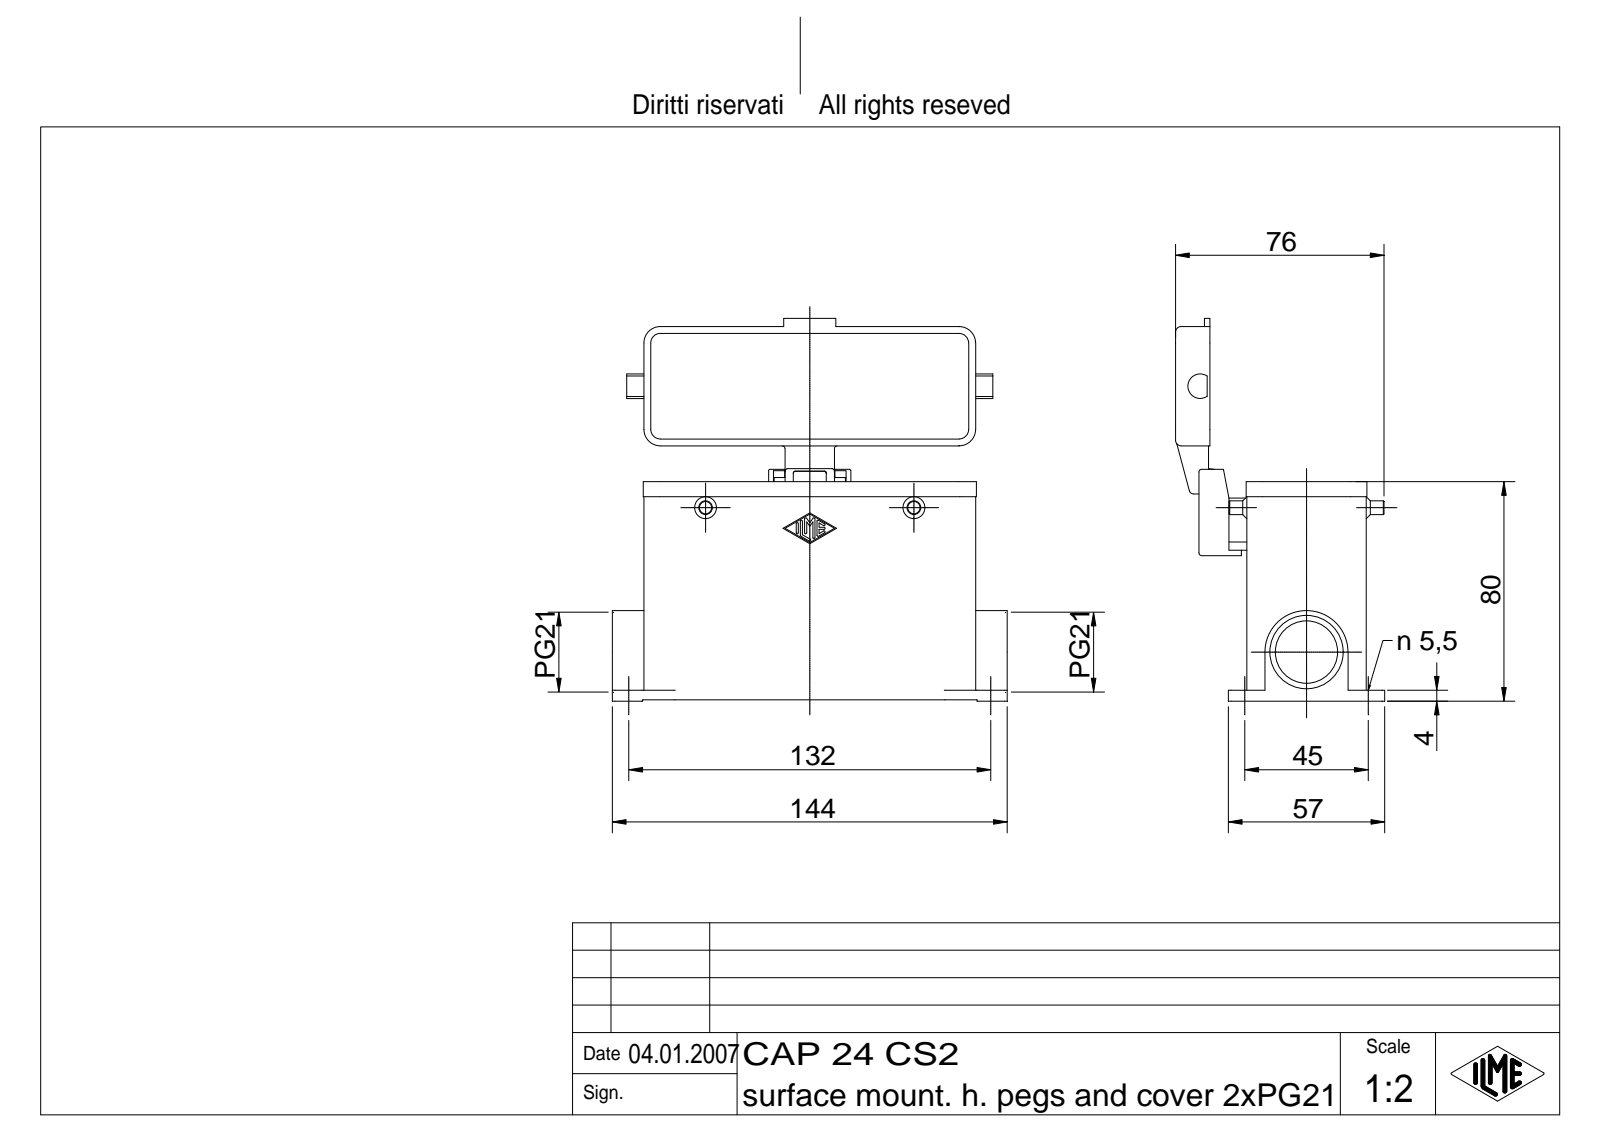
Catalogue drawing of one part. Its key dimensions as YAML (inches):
part_name: "CAP 24 CS2"
step_written_by: "Autodesk Inventor 7 (AUTOMOTIVE_DESIGN)"
units: inches
bodies: {solids: 2, faces: 474, planar: 177, cylindrical: 177, other: 120}
overall_size: [5.669, 5.492, 3.002]
volume: 9.798
surface_area: 136.9
round_holes:
  - {diameter: 0.217, count: 4}
  - {diameter: 0.157, count: 1}
  - {diameter: 0.197, count: 1}
  - {diameter: 0.897, count: 1}
  - {diameter: 1.054, count: 1}
round_bosses_or_shafts:
  - {diameter: 0.197, count: 2}
  - {diameter: 0.118, count: 2}
  - {diameter: 0.276, count: 1}
  - {diameter: 0.157, count: 1}
partial_cylinders:
  - {radius: 0.039, count: 26}
  - {radius: 0.015, count: 14}
  - {radius: 0.236, count: 12}
  - {radius: 0.02, count: 9}
  - {radius: 0.028, count: 8}
  - {radius: 0.079, count: 8}
  - {radius: 0.118, count: 4}
  - {radius: 0.138, count: 4}
face_to_face_distances: [0.118, 1.594, 1.713, 0.138, 1.476, 2.736, 2.618, 0.886, 1.142, 1.024]
hole_center_spacings: [1.772, 5.197, 5.491]
